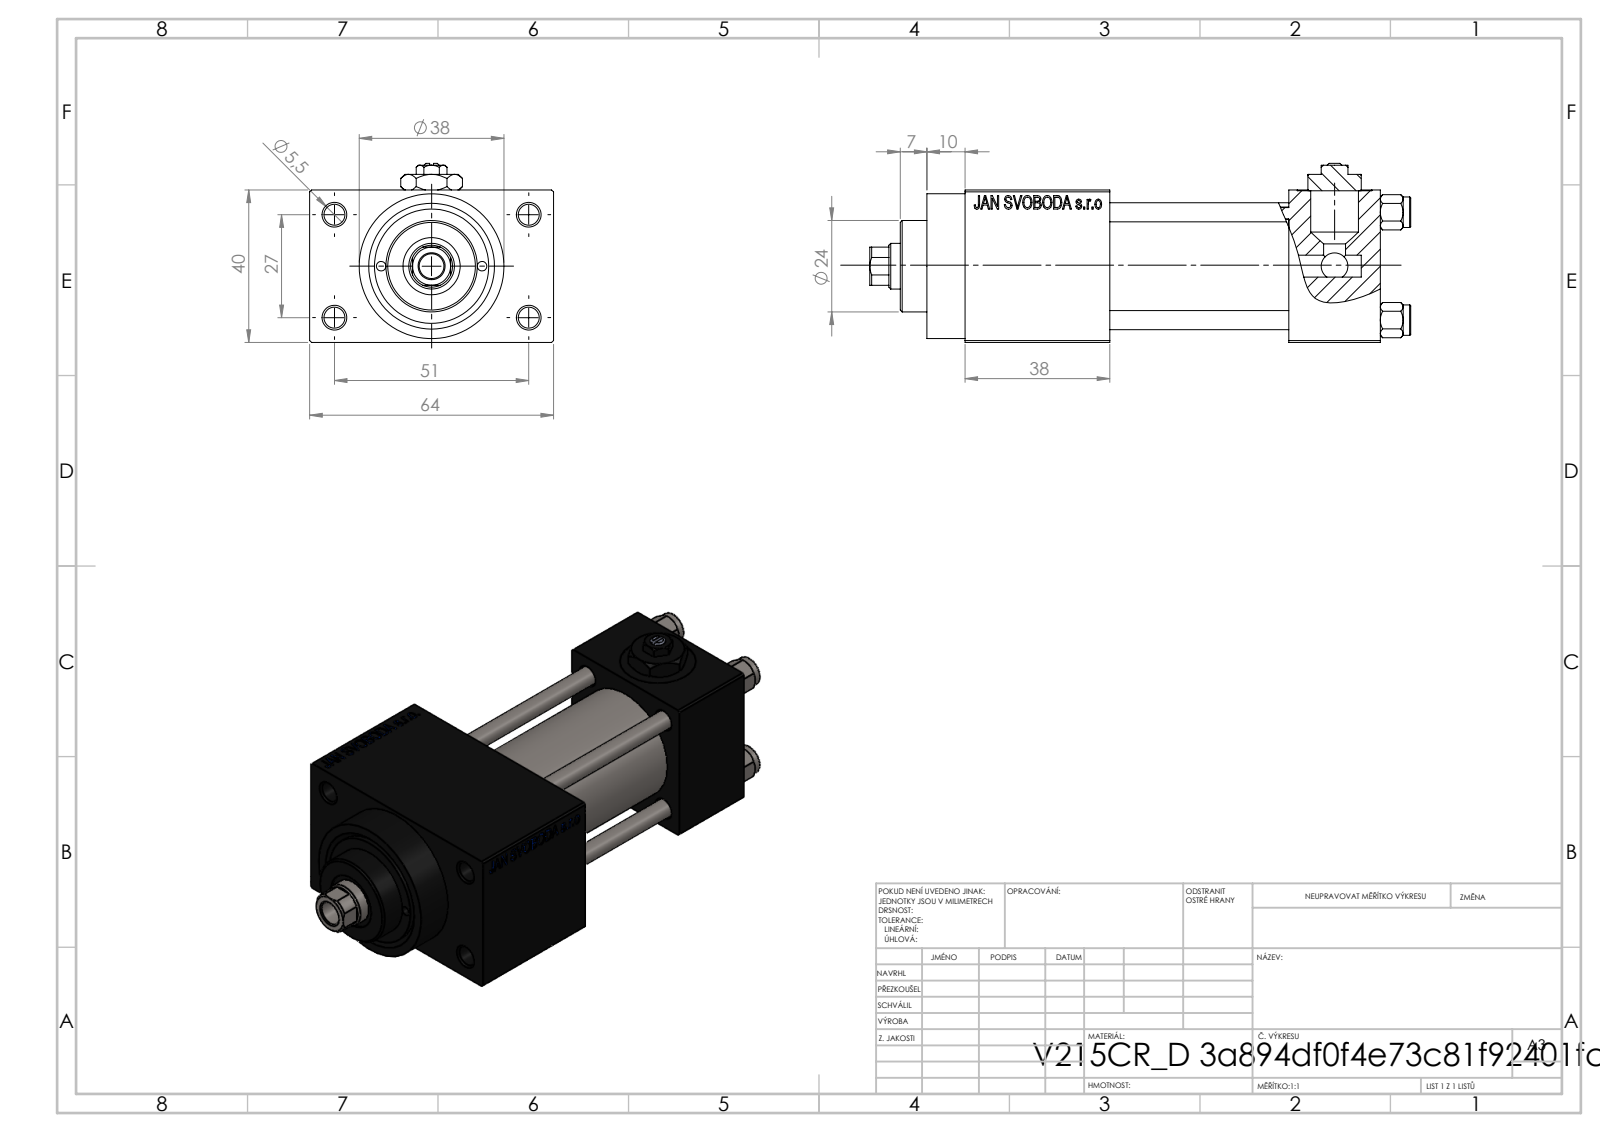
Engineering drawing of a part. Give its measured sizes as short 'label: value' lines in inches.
name: NUT_M5_D; Zatka_pro_OIL_PORT; V215CR_D_Body; V215CR_D_TYCINKA (+2 more)
written by: SolidWorks 2019 (CONFIG_CONTROL_DESIGN)
unit: in
bodies: 12 solids, 1162 faces (521 planar, 99 cylindrical, 542 other)
size: 5.591 × 2.52 × 1.85
volume: 10.52 in³; area: 98.03 in²
holes: 4× ⌀0.197, 4× ⌀0.217, 4× ⌀0.787, 3× ⌀0.276, 3× ⌀0.518, 2× ⌀0.098, 1× ⌀0.256, 1× ⌀0.472, 1× ⌀0.591, 1× ⌀0.984, 1× ⌀1.181
bosses: 4× ⌀0.315, 1× ⌀1.496, 1× ⌀1.22, 1× ⌀0.945
rounds: 1× R0.217
face distances: 1.575, 0.472, 1.85, 2.047, 0.945, 2.795, 1.496, 4.291, 3.346, 2.52
hole spacings: 0.448, 0.558, 0.718, 0.788, 1.114, 1.136, 1.177, 1.214
